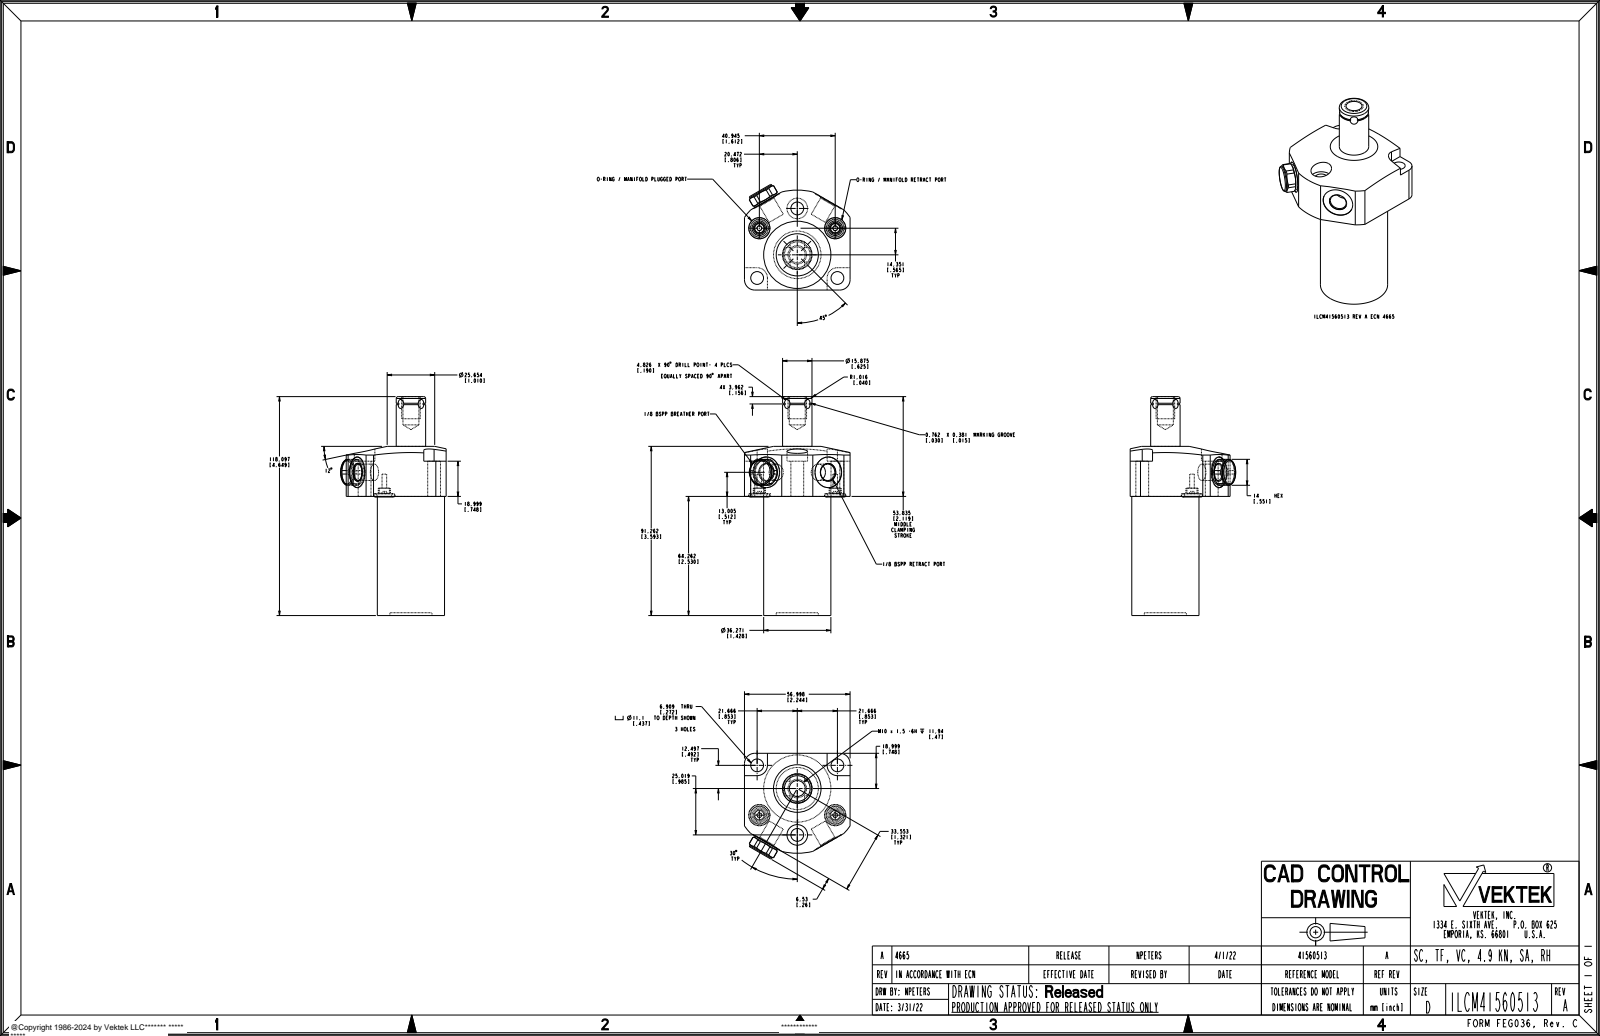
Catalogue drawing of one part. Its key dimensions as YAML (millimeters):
part_name: "ILCM41560513"
step_written_by: "CREO PARAMETRIC BY PTC INC, 2021164 (AUTOMOTIVE_DESIGN)"
units: millimeters
bodies: {solids: 1, faces: 165, planar: 64, cylindrical: 65, other: 36}
overall_size: [118.1, 62.08, 60.27]
volume: 135224
surface_area: 22918
round_holes:
  - {diameter: 6.91, count: 3}
  - {diameter: 2.49, count: 2}
  - {diameter: 6.5, count: 2}
  - {diameter: 8.84, count: 2}
  - {diameter: 11.4, count: 2}
  - {diameter: 16.51, count: 2}
  - {diameter: 8.61, count: 1}
  - {diameter: 11.1, count: 1}
  - {diameter: 22.73, count: 1}
round_bosses_or_shafts:
  - {diameter: 5.49, count: 2}
  - {diameter: 36.27, count: 1}
  - {diameter: 15.88, count: 1}
  - {diameter: 13.77, count: 1}
  - {diameter: 10.01, count: 1}
partial_cylinders:
  - {radius: 5.55, count: 2}
  - {radius: 5.56, count: 2}
  - {radius: 7.56, count: 1}
  - {radius: 7.6, count: 1}
  - {radius: 34.92, count: 1}
face_to_face_distances: [57, 64.26, 1.52, 62.74, 91.26, 89.74, 27, 83.26, 81.74, 19]
hole_center_spacings: [25.02, 23.08, 25, 26.88, 43.33, 49.97, 40.94, 43.34]
